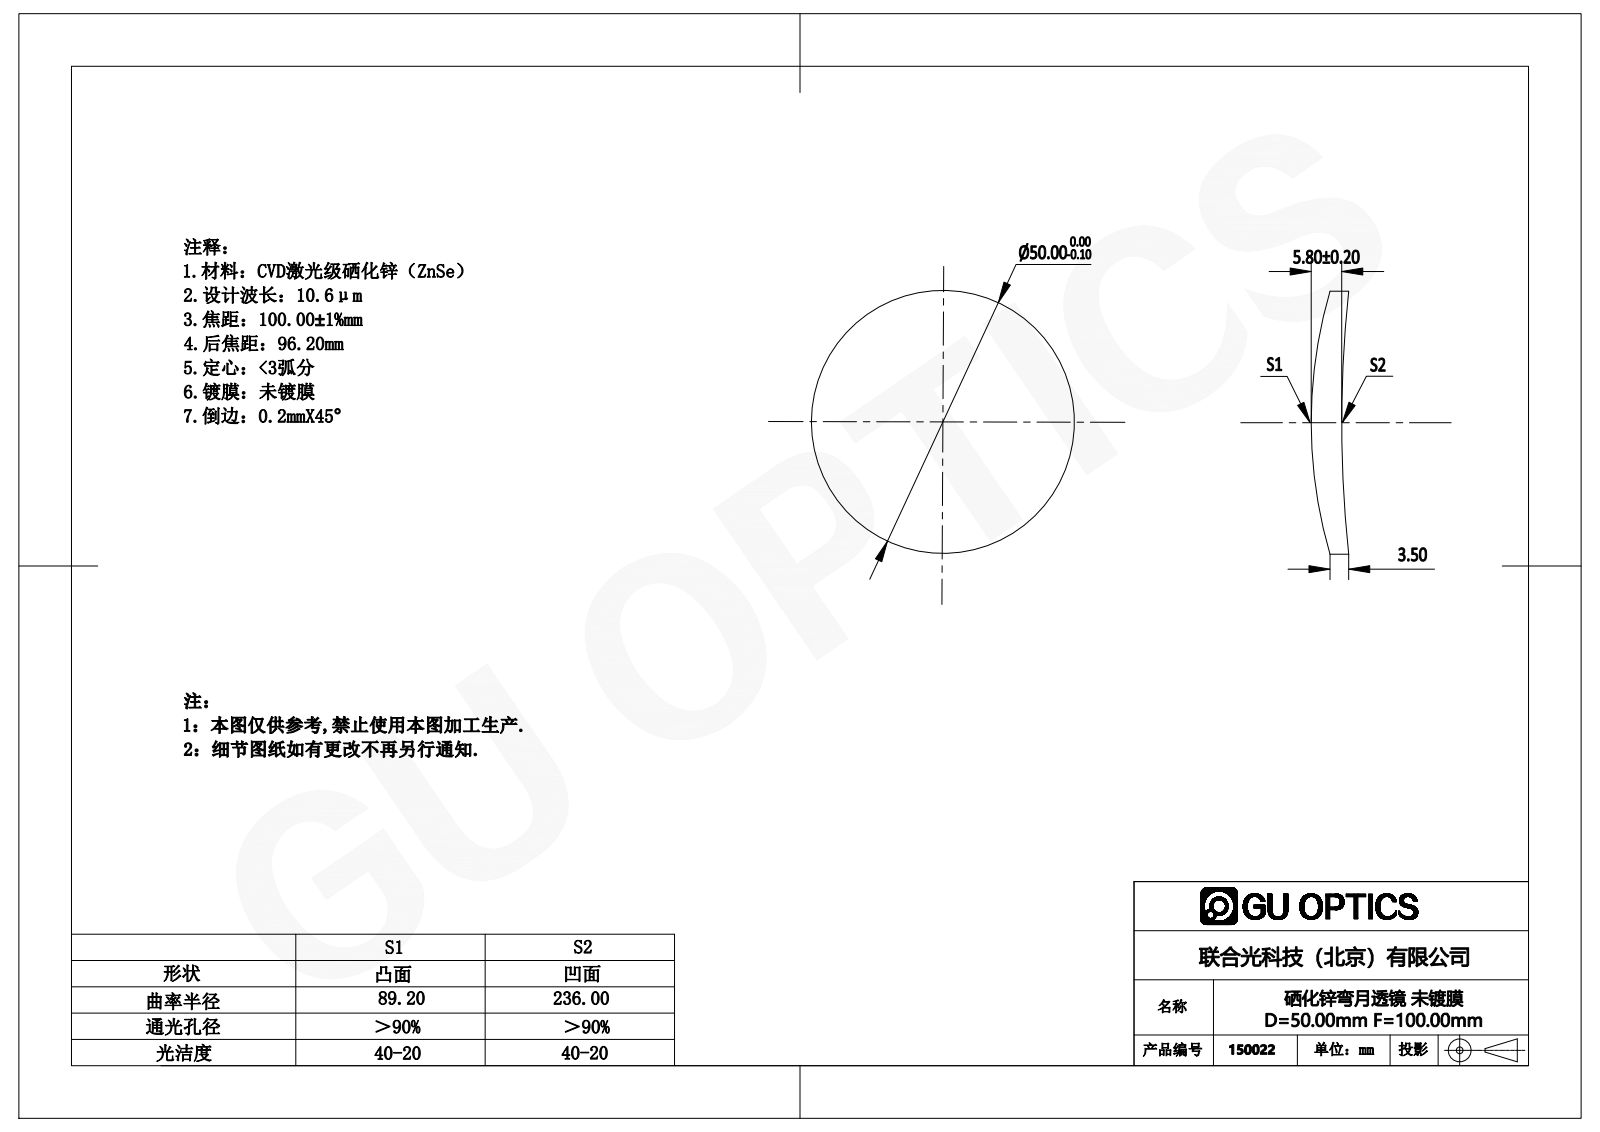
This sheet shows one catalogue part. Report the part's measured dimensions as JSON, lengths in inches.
{"part_name": "150022", "step_written_by": "SolidWorks 2016 (AUTOMOTIVE_DESIGN)", "units": "inches", "bodies": {"solids": 1, "faces": 6, "planar": 0, "cylindrical": 2, "other": 4}, "overall_size": [1.969, 1.969, 0.281], "volume_in3": 0.562, "surface_area_in2": 7.023, "round_bosses_or_shafts": [[1.969, 1]]}
